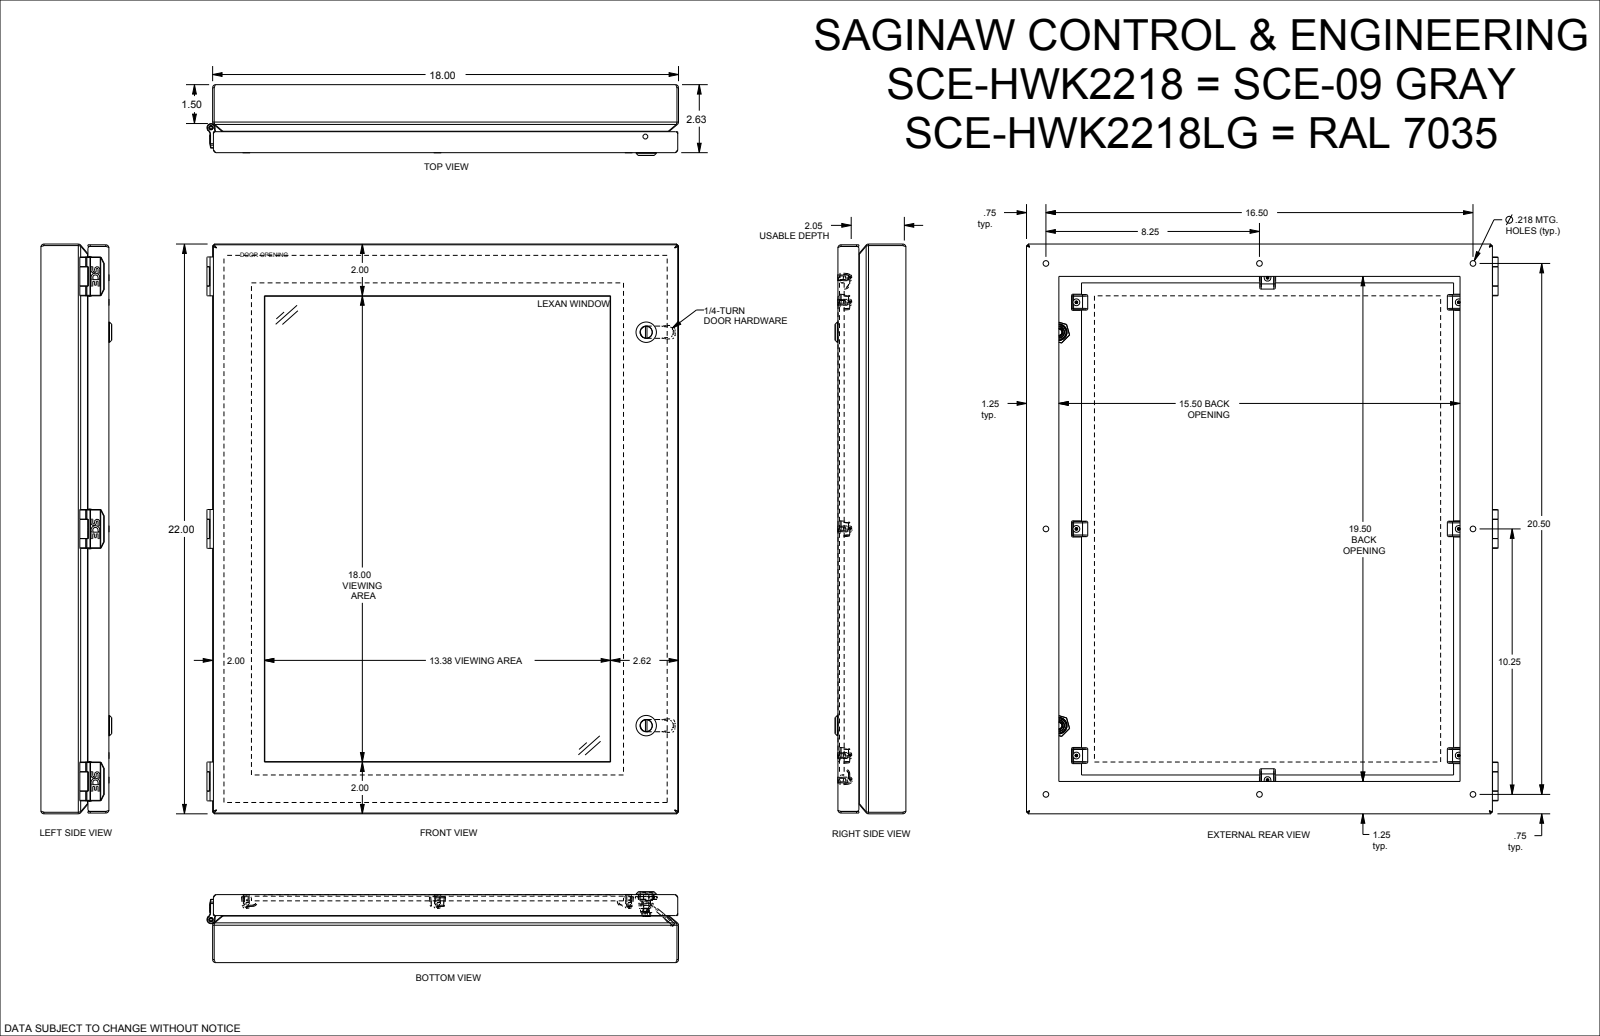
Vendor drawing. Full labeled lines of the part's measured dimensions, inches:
Part name (STEP PRODUCT): SCE-HWK2218
STEP written by: SolidWorks 2021 (AUTOMOTIVE_DESIGN)
Units: inches
Bodies: 59 solids, 2882 faces (1187 planar, 787 cylindrical, 908 other)
Overall size (bounding box): 22 × 18.22 × 2.733
Volume: 112 in³ · Surface area: 2 137 in²
Round holes (diameter × count): ⌀0.138 ×8, ⌀0.156 ×8, ⌀0.213 ×8, ⌀0.218 ×8, ⌀0.164 ×3, ⌀0.17 ×3, ⌀0.174 ×3, ⌀0.266 ×3, ⌀0.338 ×3, ⌀0.2 ×2, ⌀0.239 ×2, ⌀0.254 ×2
Round bosses / shafts (diameter × count): ⌀0.262 ×8, ⌀0.212 ×8, ⌀0.479 ×3, ⌀0.26 ×3, ⌀0.15 ×3, ⌀0.788 ×2, ⌀0.548 ×2, ⌀0.46 ×2
Partial cylindrical surfaces — rounded edges, fillets, slot ends (radius × count): R0.106 ×99, R0.005 ×54, R0.008 ×48, R0.02 ×44, R0.05 ×44, R0.025 ×18, R0.01 ×16, R0.06 ×16
Main face-to-face distances: 0.06, 0.181, 0.241, 0.059, 0.236, 0.055, 0.03, 0.029, 2.385, 2.566
Hole centre spacings: 7.446, 8.246, 8.75, 9.75, 10.246, 12.189, 13.152, 17.167
